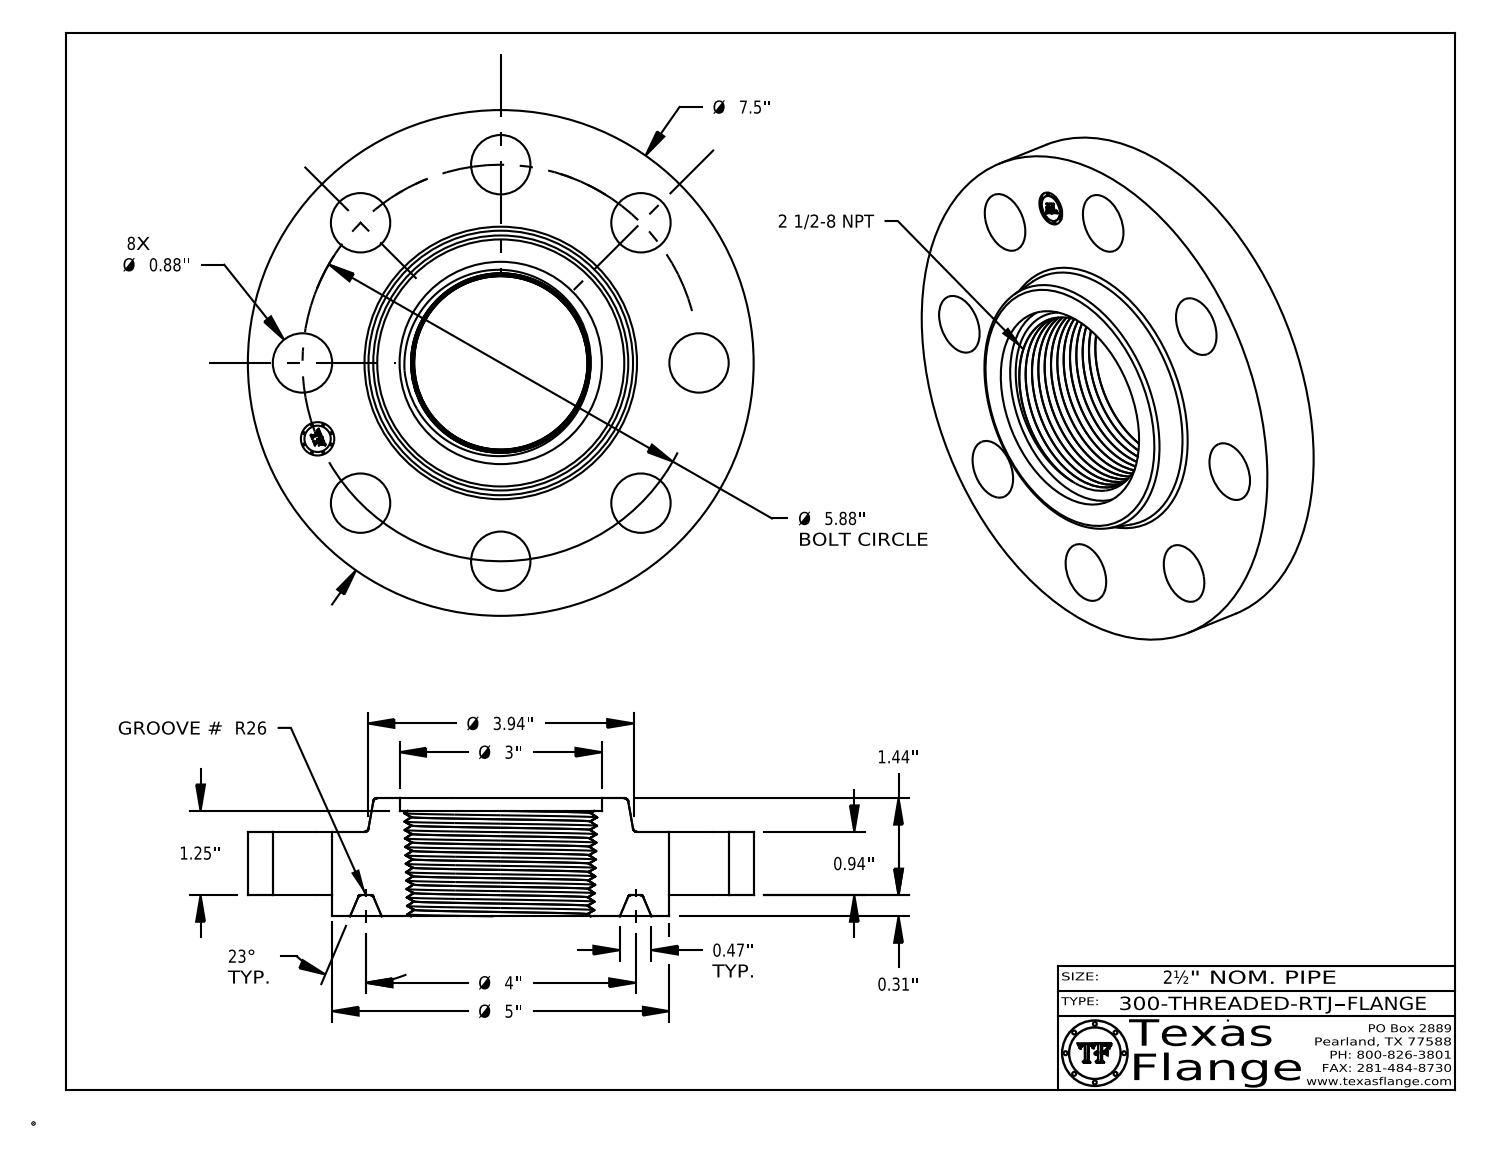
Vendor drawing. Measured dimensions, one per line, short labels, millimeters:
name: 300-THREADED-RTJ
written by: CATIA V5 STEP AP214 (AUTOMOTIVE_DESIGN)
unit: mm
bodies: 1 solid, 560 faces (372 planar, 42 cylindrical, 146 other)
size: 190.5 × 190.5 × 44.5
volume: 609 900 mm³; area: 97 740 mm²
holes: 8× ⌀22.4, 1× ⌀12.6, 1× ⌀76.2
bosses: 8× ⌀0.8, 1× ⌀190.5, 1× ⌀127, 1× ⌀9.9
face distances: 23.9, 8, 31.8, 44.5, 36.6, 12.7, 39.7, 31.8, 7.9, 4.8
hole spacings: 57.2, 138, 74.7, 74.7, 105.6, 105.6, 83, 149.4
